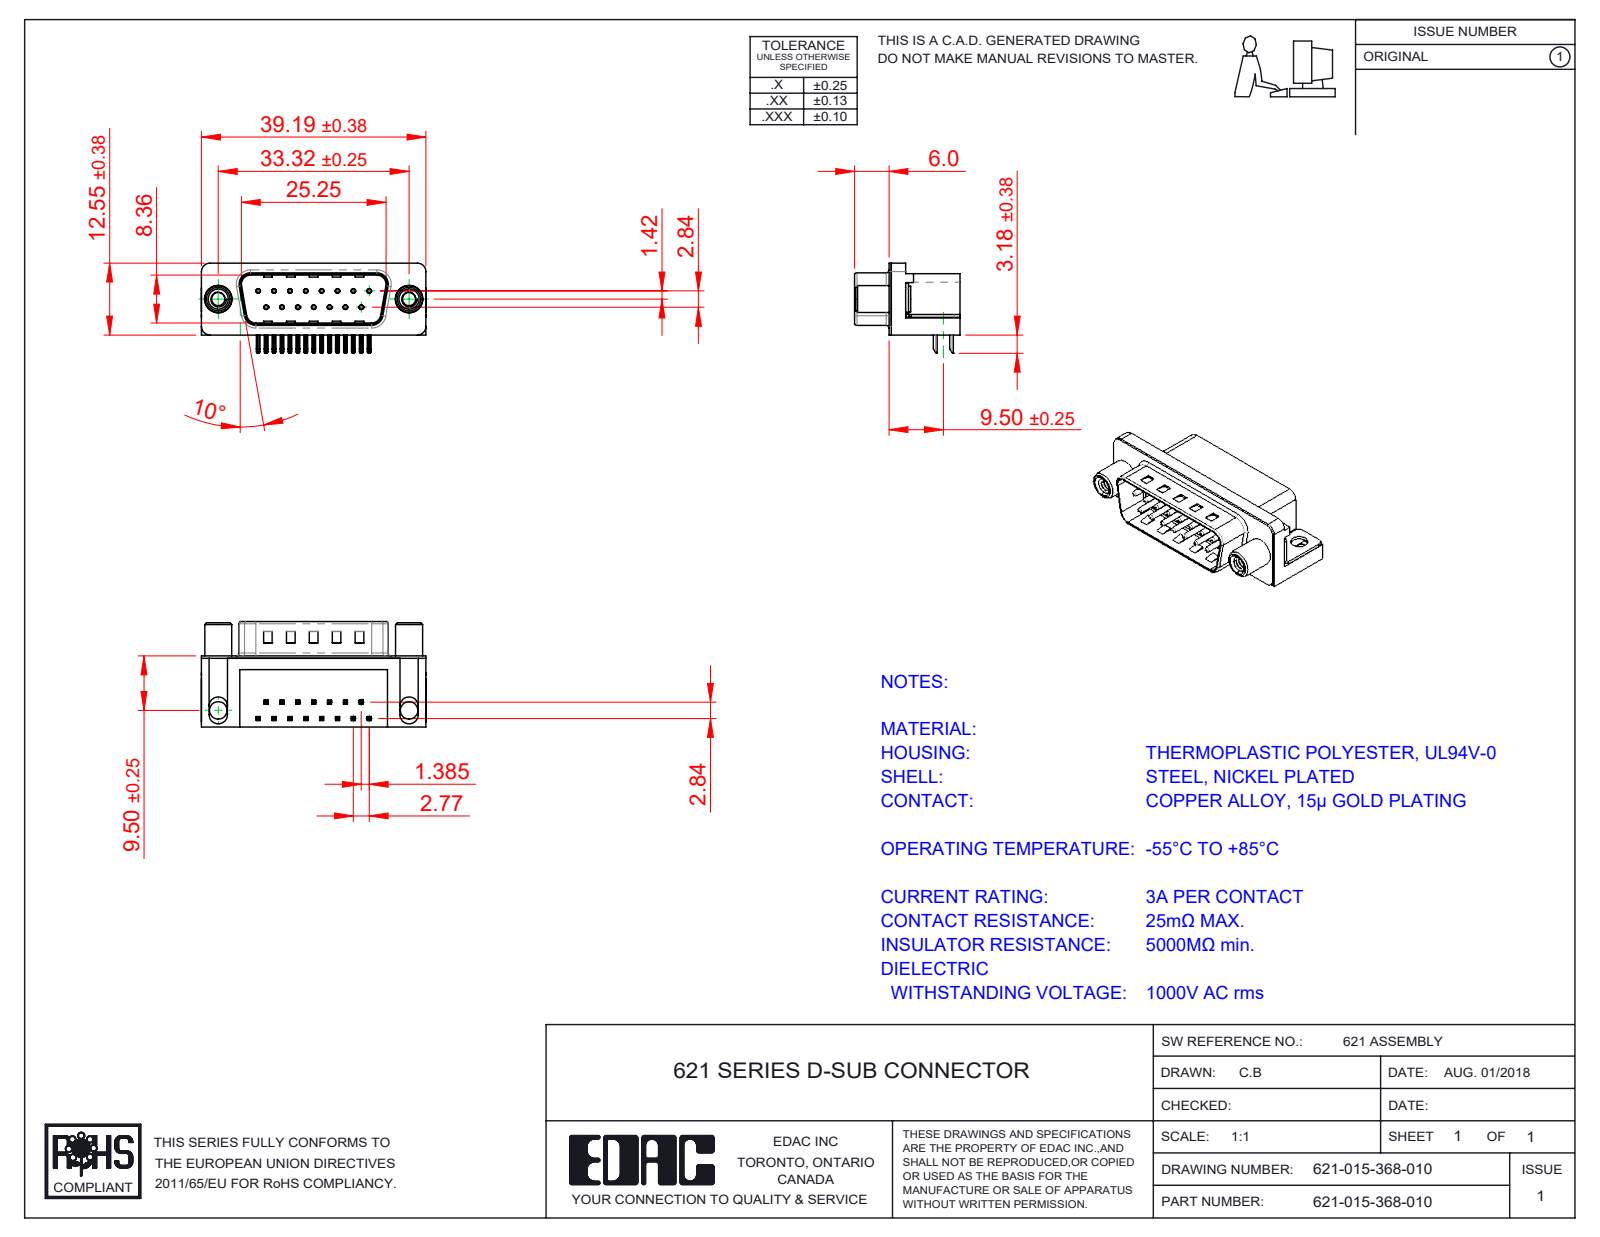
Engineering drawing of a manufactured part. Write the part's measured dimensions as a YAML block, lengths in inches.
part_name: "621 Housing_15 Socket; 621-015-368-010; 621 Contact Top; 621 Thru Hole Board Mount (+3 more)"
step_written_by: "SolidWorks 2016 (CONFIG_CONTROL_DESIGN)"
units: inches
bodies: {solids: 21, faces: 1469, planar: 883, cylindrical: 453, other: 133}
overall_size: [1.544, 0.724, 0.619]
volume: 0.275
surface_area: 9.046
round_holes:
  - {diameter: 0.014, count: 15}
  - {diameter: 0.031, count: 15}
  - {diameter: 0.091, count: 2}
  - {diameter: 0.12, count: 2}
  - {diameter: 0.122, count: 2}
  - {diameter: 0.157, count: 2}
  - {diameter: 0.189, count: 2}
  - {diameter: 0.197, count: 2}
round_bosses_or_shafts:
  - {diameter: 0.03, count: 15}
  - {diameter: 0.193, count: 2}
  - {diameter: 0.185, count: 2}
  - {diameter: 0.177, count: 2}
  - {diameter: 0.152, count: 2}
partial_cylinders:
  - {radius: 0.01, count: 60}
  - {radius: 0.005, count: 30}
  - {radius: 0.039, count: 16}
  - {radius: 0.02, count: 9}
  - {radius: 0.063, count: 8}
  - {radius: 0.059, count: 6}
  - {radius: 0.035, count: 4}
  - {radius: 0.079, count: 4}
face_to_face_distances: [0.016, 0.472, 0.407, 0.083, 0.412, 0.067, 0.488, 0.428, 0.345, 0.114]
hole_center_spacings: [0.124, 0.109, 0.218, 0.327, 0.436, 0.198, 0.198, 0.294]
